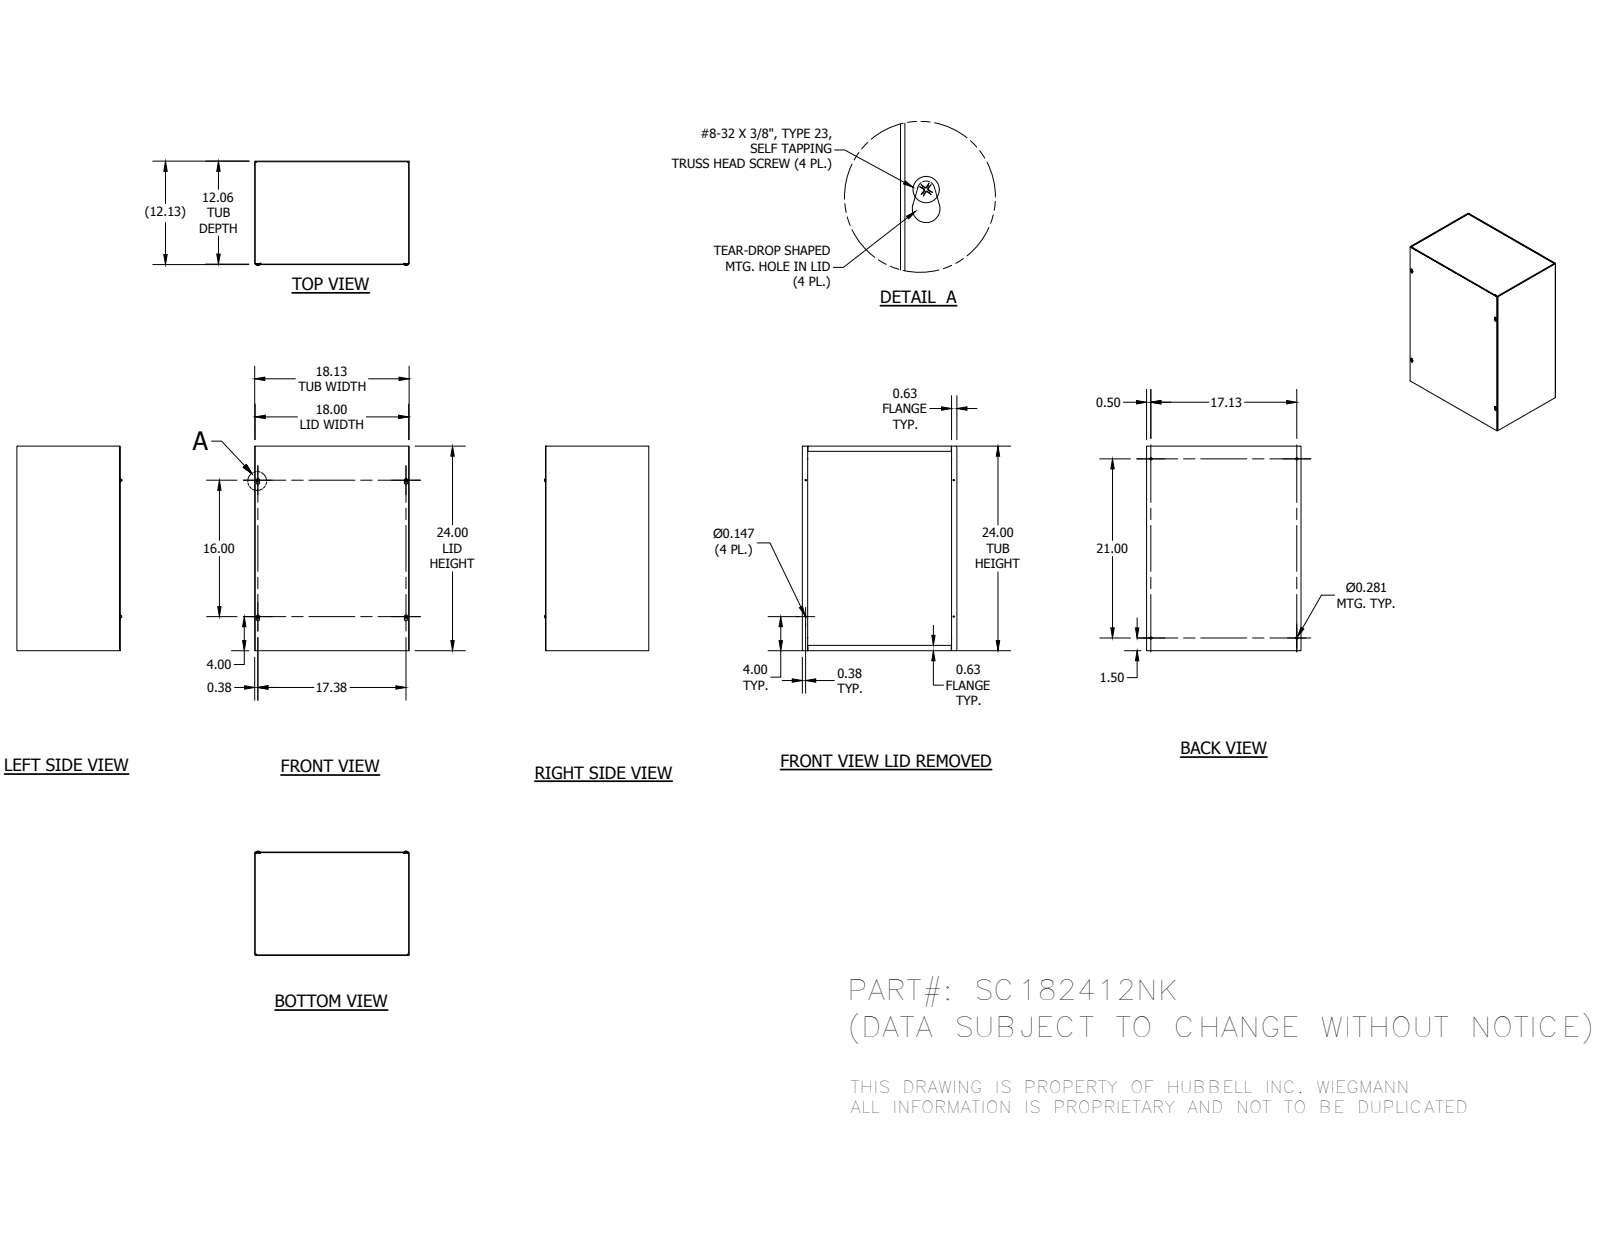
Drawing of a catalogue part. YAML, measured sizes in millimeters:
part_name: "SC182412NKBLR; SC1812NKTB; SC1824LPA; 34056 (+1 more)"
step_written_by: "Autodesk Inventor 2014 (AUTOMOTIVE_DESIGN)"
units: millimeters
bodies: {solids: 8, faces: 268, planar: 152, cylindrical: 48, other: 68}
overall_size: [609.6, 460.38, 310.52]
volume: 2009000
surface_area: 2546000
round_holes:
  - {diameter: 3.73, count: 4}
  - {diameter: 7.14, count: 4}
round_bosses_or_shafts:
  - {diameter: 9.75, count: 4}
  - {diameter: 4.17, count: 4}
partial_cylinders:
  - {radius: 0.79, count: 12}
  - {radius: 2.38, count: 12}
  - {radius: 3.17, count: 4}
  - {radius: 5.16, count: 4}
face_to_face_distances: [1.59, 306.39, 458.79, 304.8, 307.98, 608.01, 457.2, 460.38, 609.6, 606.42]
hole_center_spacings: [63.58, 442.73, 469.91, 642.48, 406.4, 434.98, 441.32, 533.4]
